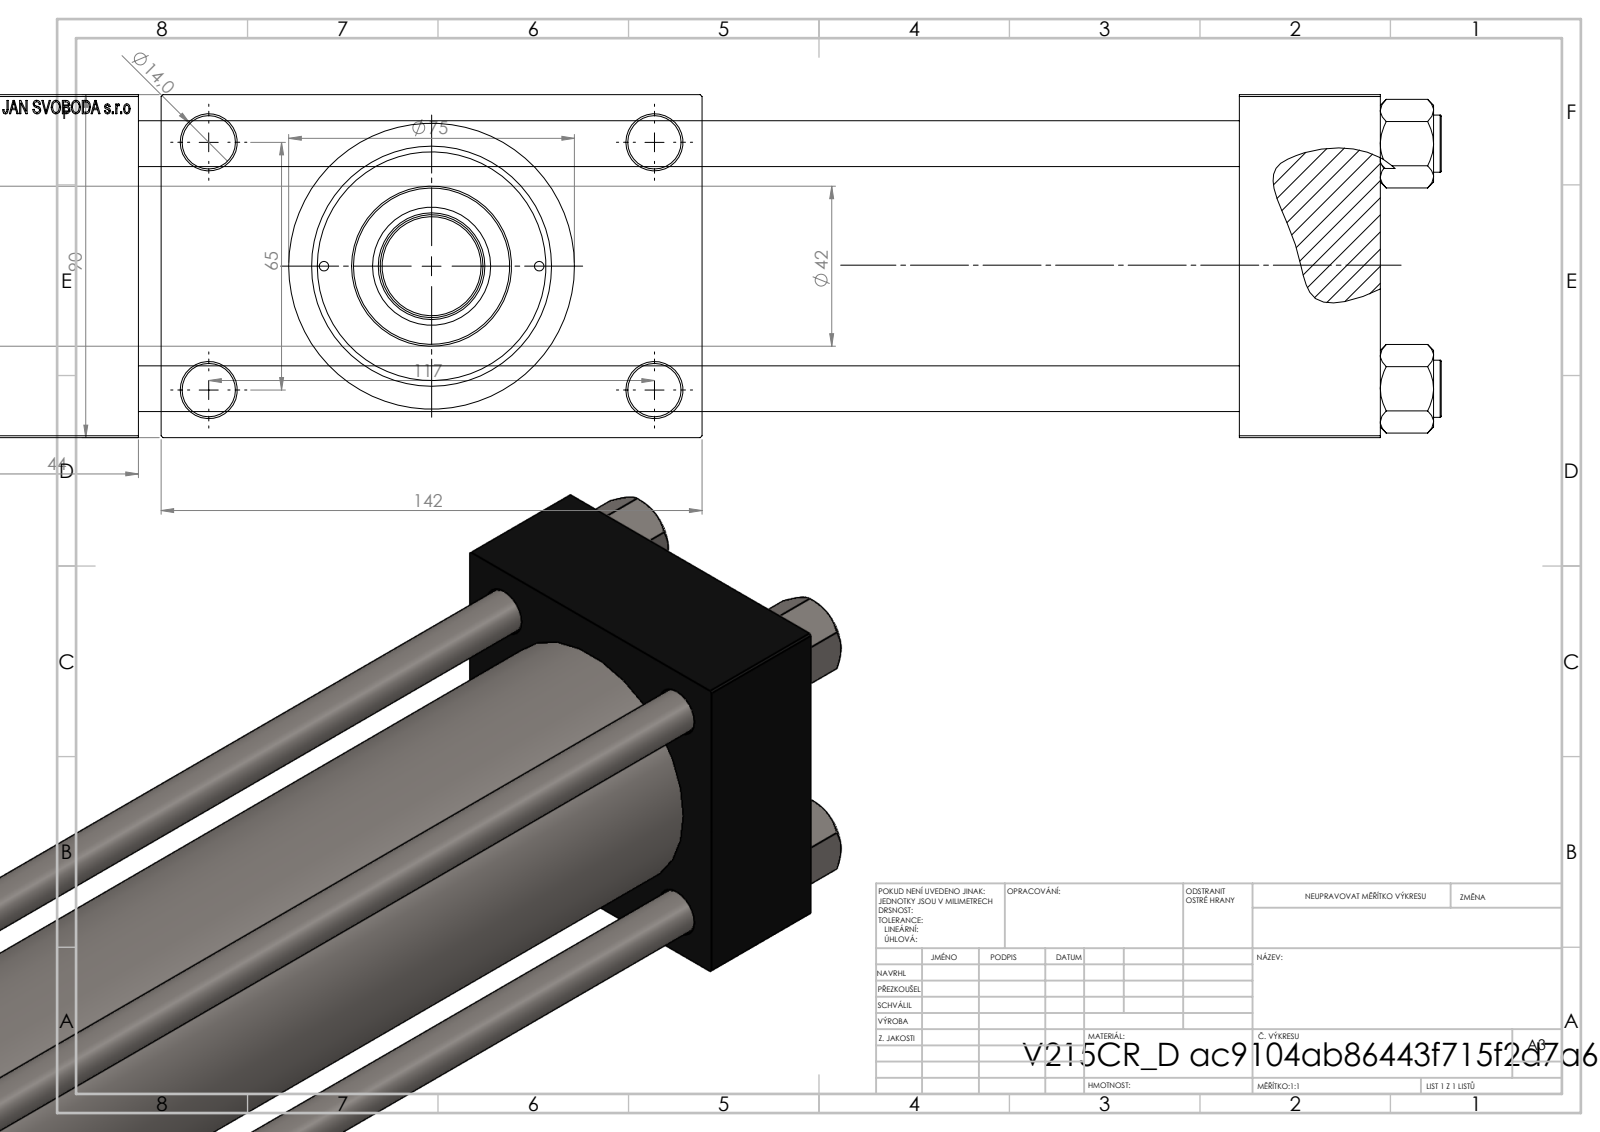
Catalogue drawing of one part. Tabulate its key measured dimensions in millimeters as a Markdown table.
| quantity | value |
| --- | --- |
| part name | V215CR_D_TYCINKA; V215CR_D_Body; V215_VC_A; V215CR_ROD_END_F (+2 more) |
| STEP written by | SolidWorks 2019 (CONFIG_CONTROL_DESIGN) |
| units | millimeters |
| bodies | 12 solids, 1125 faces (503 planar, 96 cylindrical, 526 other) |
| overall size | 461 × 142 × 90 |
| volume | 1 496 000 mm³ |
| surface area | 353 780 mm² |
| round holes (diameter × count) | 12 × 4, 14 × 4, 2.5 × 2, 7 × 2, 20.96 × 2, 30 × 2, 18.5 × 1, 28 × 1, 31 × 1, 50 × 1, 60 × 1, 63 × 1 |
| round bosses / shafts (diameter × count) | 15 × 4, 75 × 1, 69 × 1, 42 × 1, 27 × 1, 18 × 1 |
| main face-to-face distances | 90, 289, 37, 326, 333, 370, 44, 26, 116, 16 |
| hole center spacings | 26.35, 32.39, 44.4, 45.47, 64.3, 66.92, 68.42, 69.81 |
